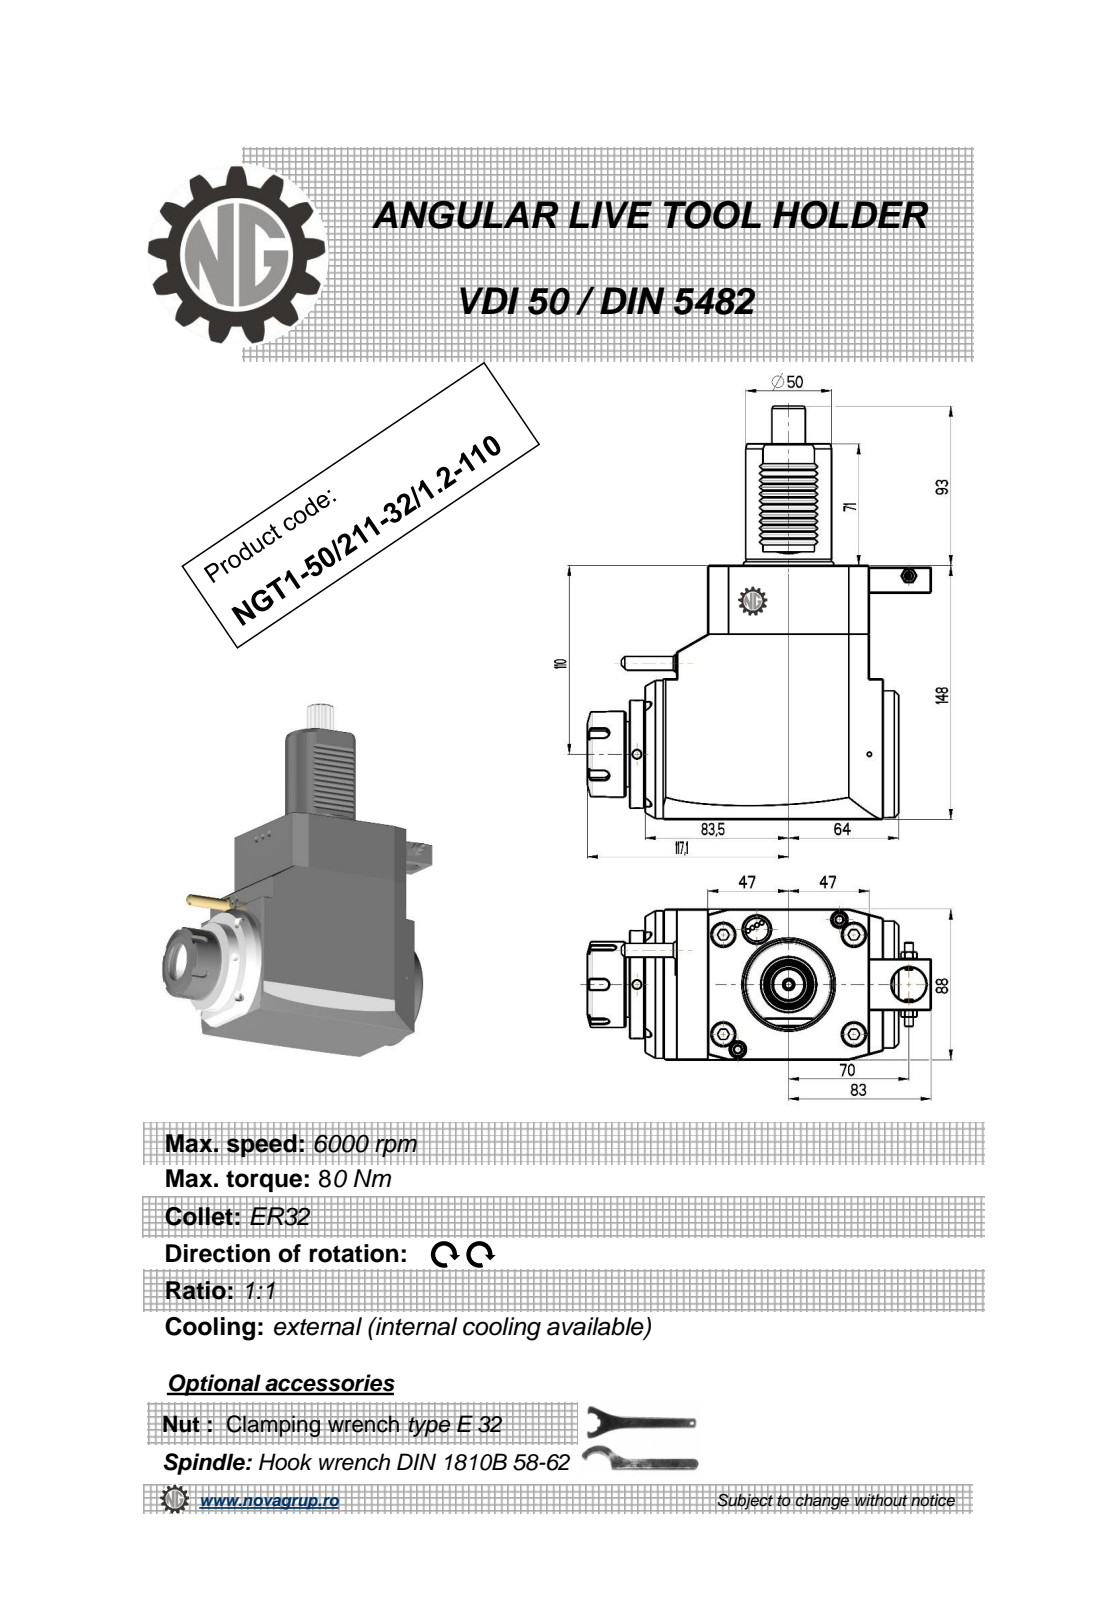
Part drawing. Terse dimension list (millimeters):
name: NGT1_50_211_32_1_2_110
written by: PRO/ENGINEER BY PARAMETRIC TECHNOLOGY CORPORATION, 2010280 (CONFIG_CONTROL_DESIGN)
unit: mm
bodies: 1 solid, 476 faces (191 planar, 141 cylindrical, 144 other)
size: 241 × 200.1 × 88
volume: 1 799 000 mm³; area: 112 472 mm²
holes: 3× ⌀5, 1× ⌀3, 1× ⌀4.2, 1× ⌀4.5, 1× ⌀5.3, 1× ⌀9.5, 1× ⌀20, 1× ⌀27
bosses: 2× ⌀50, 1× ⌀86, 1× ⌀74, 1× ⌀63, 1× ⌀50.5, 1× ⌀41, 1× ⌀10, 1× ⌀8.96
rounds: 24× R3.33, 12× R0.26, 12× R0.3, 6× R0.2, 5× R3, 1× R2.5, 1× R8.25, 1× R9.75
face distances: 88, 148, 147.5, 9, 17, 8, 94, 111, 36.5, 130.5
hole spacings: 52.46, 56.65, 70, 88.25, 101.5, 158.25
